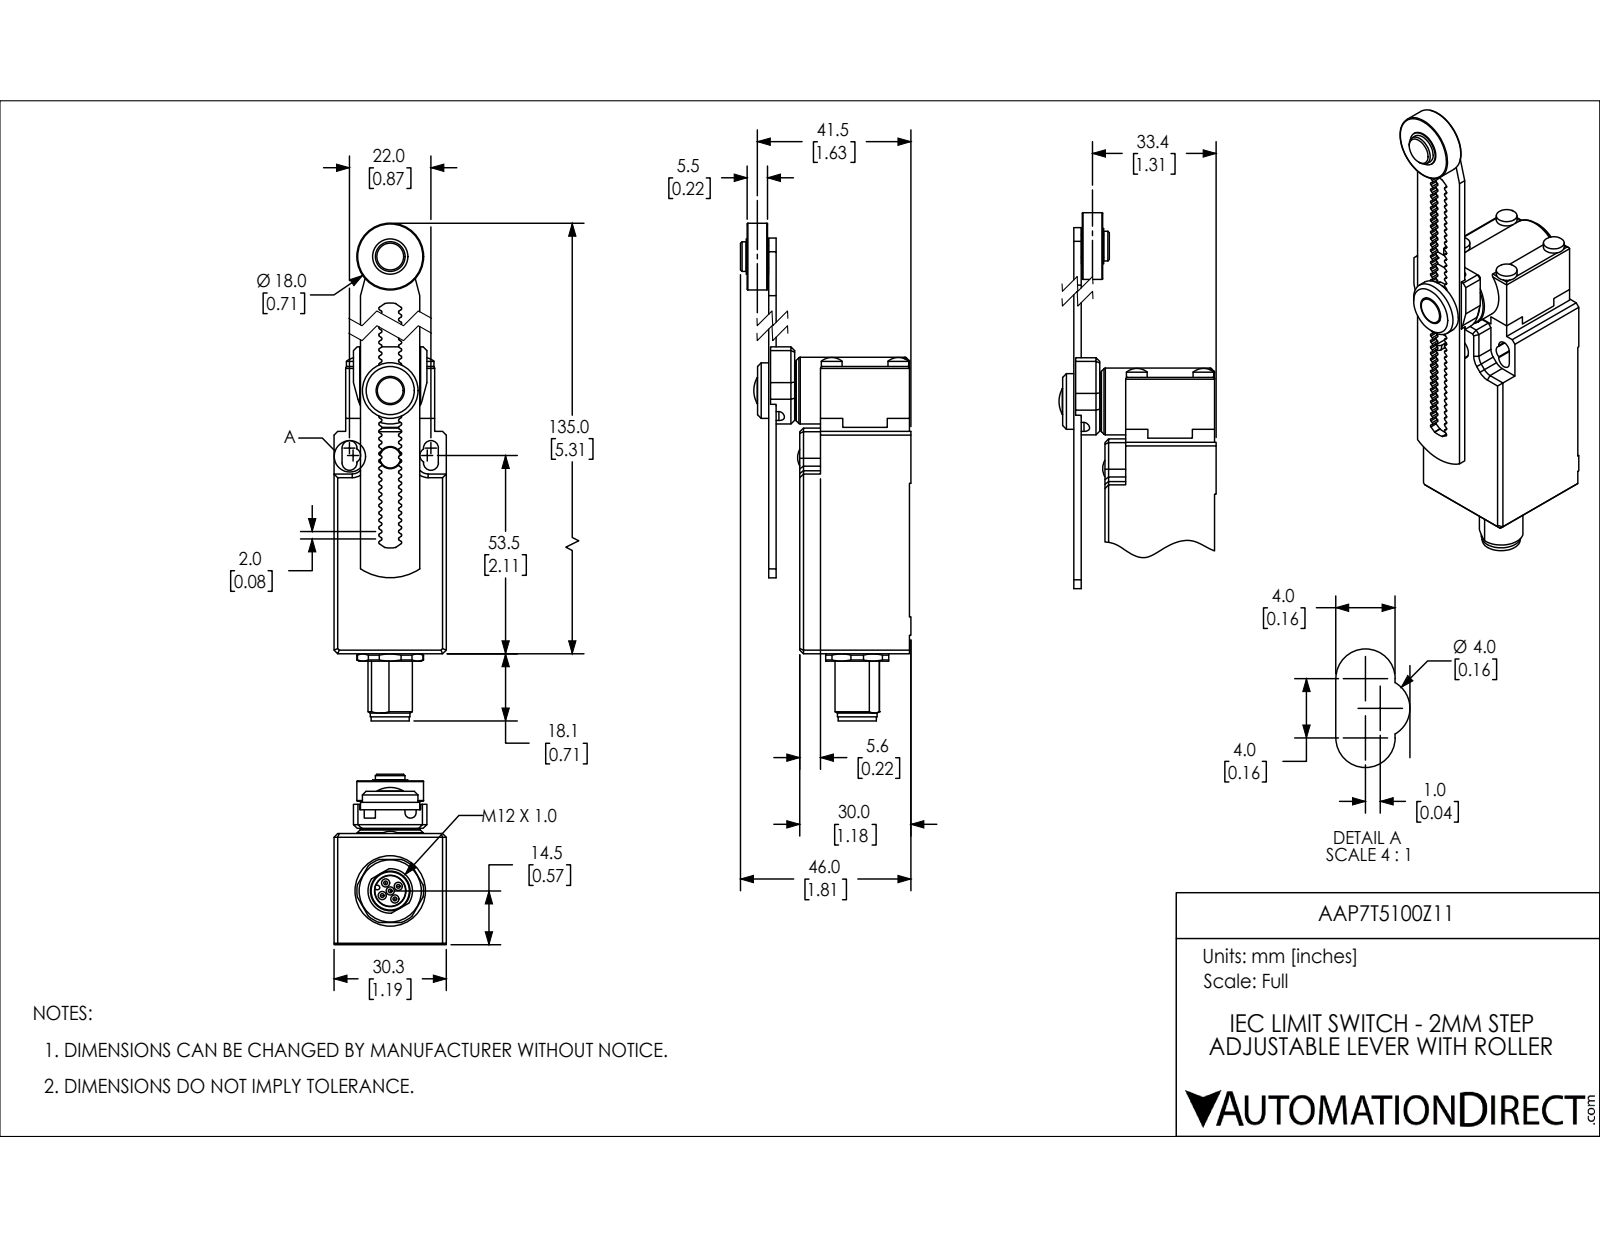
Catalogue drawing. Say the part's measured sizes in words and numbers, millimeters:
The part is named "AAP7T5100Z11". Its 3-D file was written by "SolidWorks 2018 (AUTOMOTIVE_DESIGN)". It is 6 solids with 911 faces: 362 planar, 483 cylindrical and 66 other. Overall it measures 153.1 by 46 by 30.3 millimeters. Its volume is 72 200 cubic millimeters and its surface area 22 340 square millimeters. Round holes: 5 of diameter 2.2, 1 of diameter 6, 1 of diameter 7.6, 1 of diameter 11, 1 of diameter 13, 1 of diameter 14, 1 of diameter 16. Round bosses or shafts: 5 of diameter 5.6, 5 of diameter 1.4, 5 of diameter 1, 2 of diameter 18, 1 of diameter 15, 1 of diameter 10.7, 1 of diameter 10.3, 1 of diameter 9.5. Partial cylindrical surfaces (rounded edges, fillets, slot ends): 166 of radius 0.4, 6 of radius 2, 4 of radius 0.2, 4 of radius 0.5, 4 of radius 3, 2 of radius 6.5, 1 of radius 0.6, 1 of radius 1.5. The main face-to-face distances are 2, 30.3, 6.4, 36, 29.6, 38, 8.4, 7, 3.1, 27.2. The hole center spacings are 2.5, 3.5, 5, 18.1.
